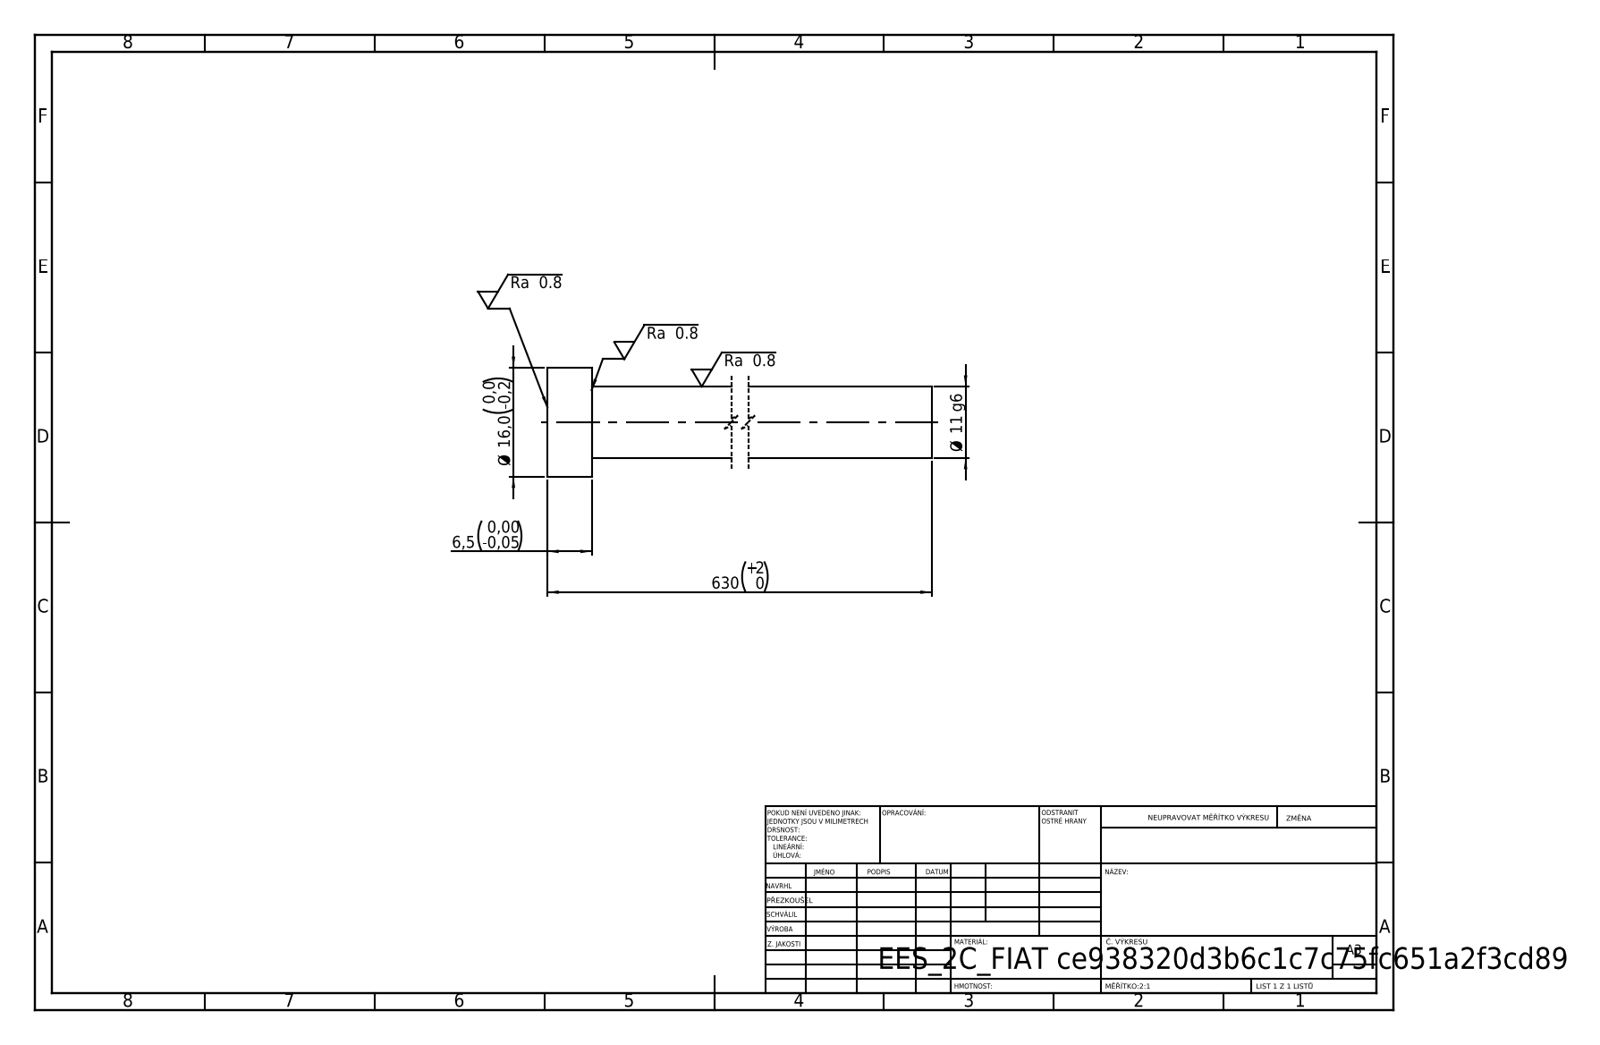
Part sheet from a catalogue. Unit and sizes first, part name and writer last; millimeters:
Units: millimetres
Overall size (bounding box): 630 × 16 × 16
Round bosses / shafts (diameter × count): ⌀16 ×1, ⌀10.5 ×1
Main face-to-face distances: 6.5, 630, 623.5
Volume: 55 296 mm³ · Surface area: 21 296 mm²
Bodies: 1 solid, 7 faces (3 planar, 4 cylindrical, 0 other)
STEP written by: SolidWorks 2019 (CONFIG_CONTROL_DESIGN)
